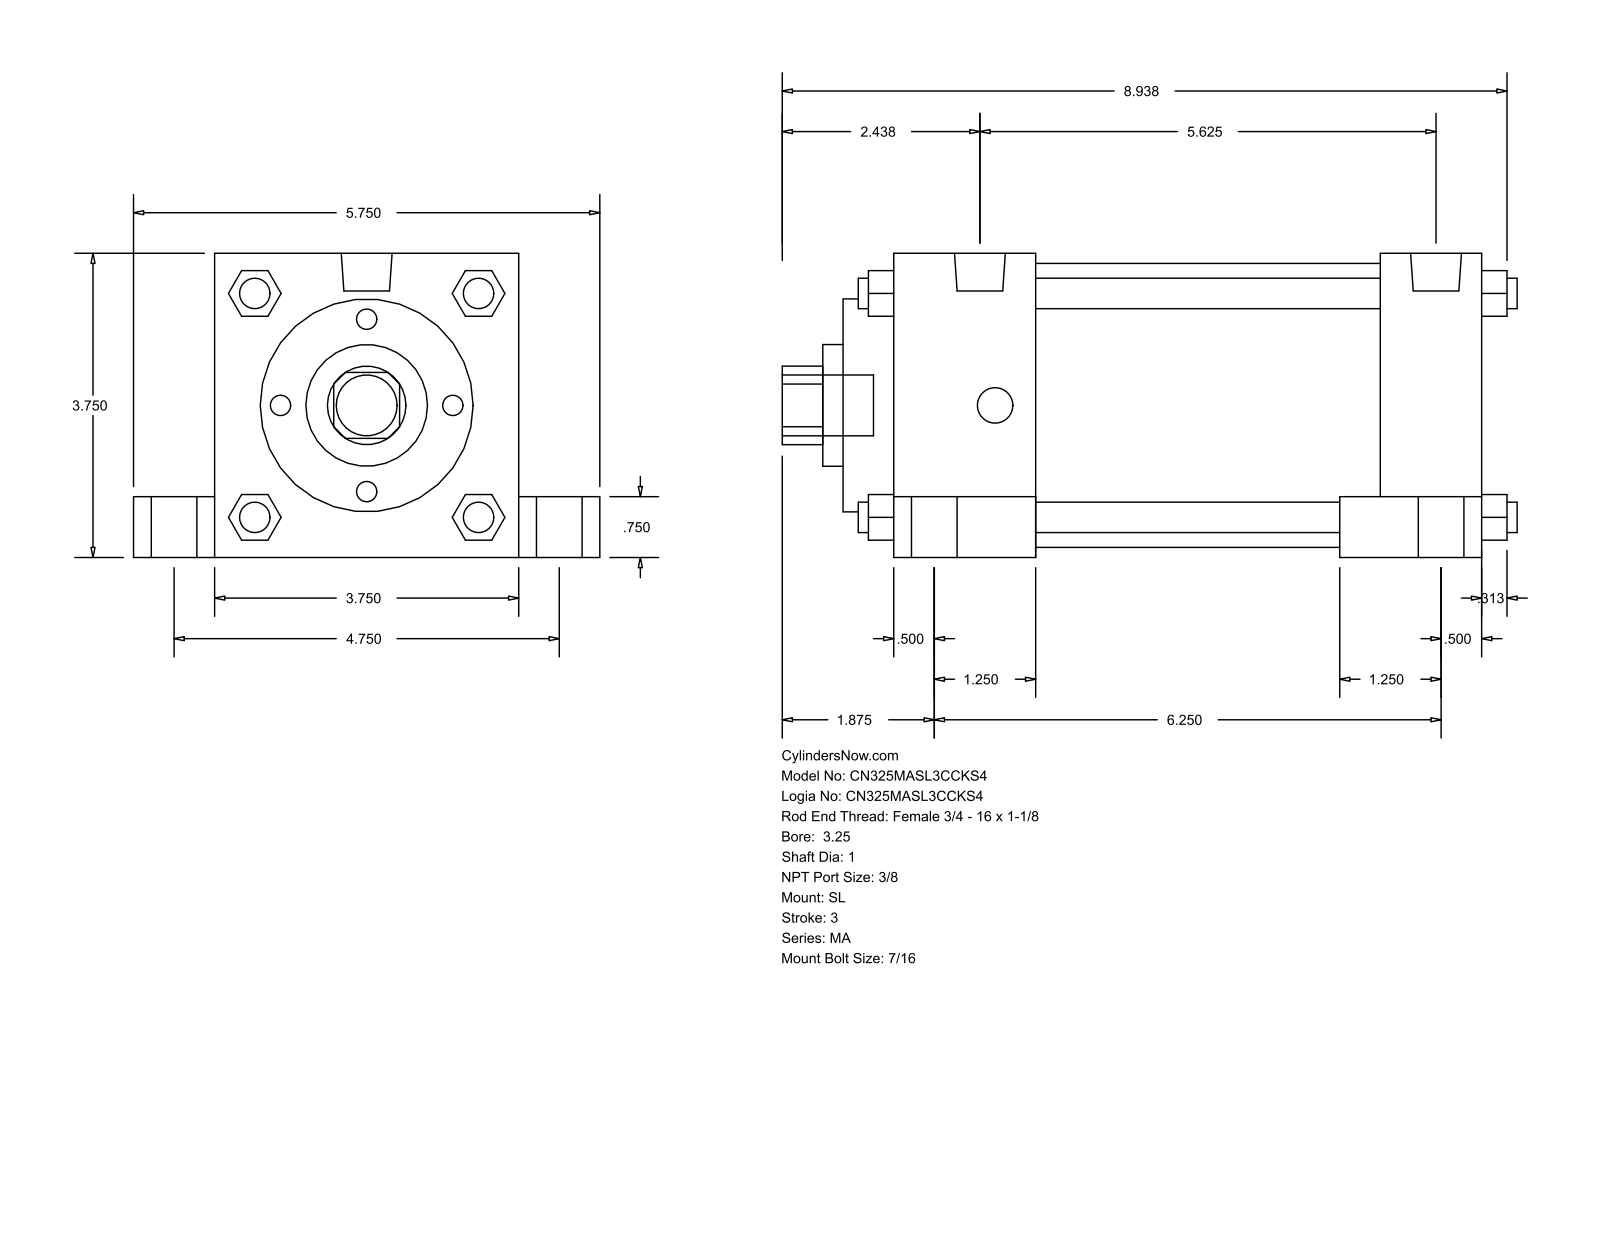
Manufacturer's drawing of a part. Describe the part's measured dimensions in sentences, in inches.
The part is named "MA_SL__0325_1". Its 3-D file was written by "GSSL Pune (CONFIG_CONTROL_DESIGN)". It is 0 solids with 150 faces: 113 planar, 37 cylindrical and 0 other. Overall it measures 9.063 by 5.75 by 3.75 inches. Round holes: 1 of diameter 1, 1 of diameter 1.5, 1 of diameter 2.625, 1 of diameter 3.5. Round bosses or shafts: 4 of diameter 0.813, 4 of diameter 0.563, 4 of diameter 0.437, 4 of diameter 0.375, 2 of diameter 0.627, 1 of diameter 0.75. Partial cylindrical surfaces (rounded edges, fillets, slot ends): 1 of radius 0.484. The main face-to-face distances are 3.75, 7.25, 0.625, 1, 4.75, 7.875, 0.75, 6, 1.25, 1.75.
